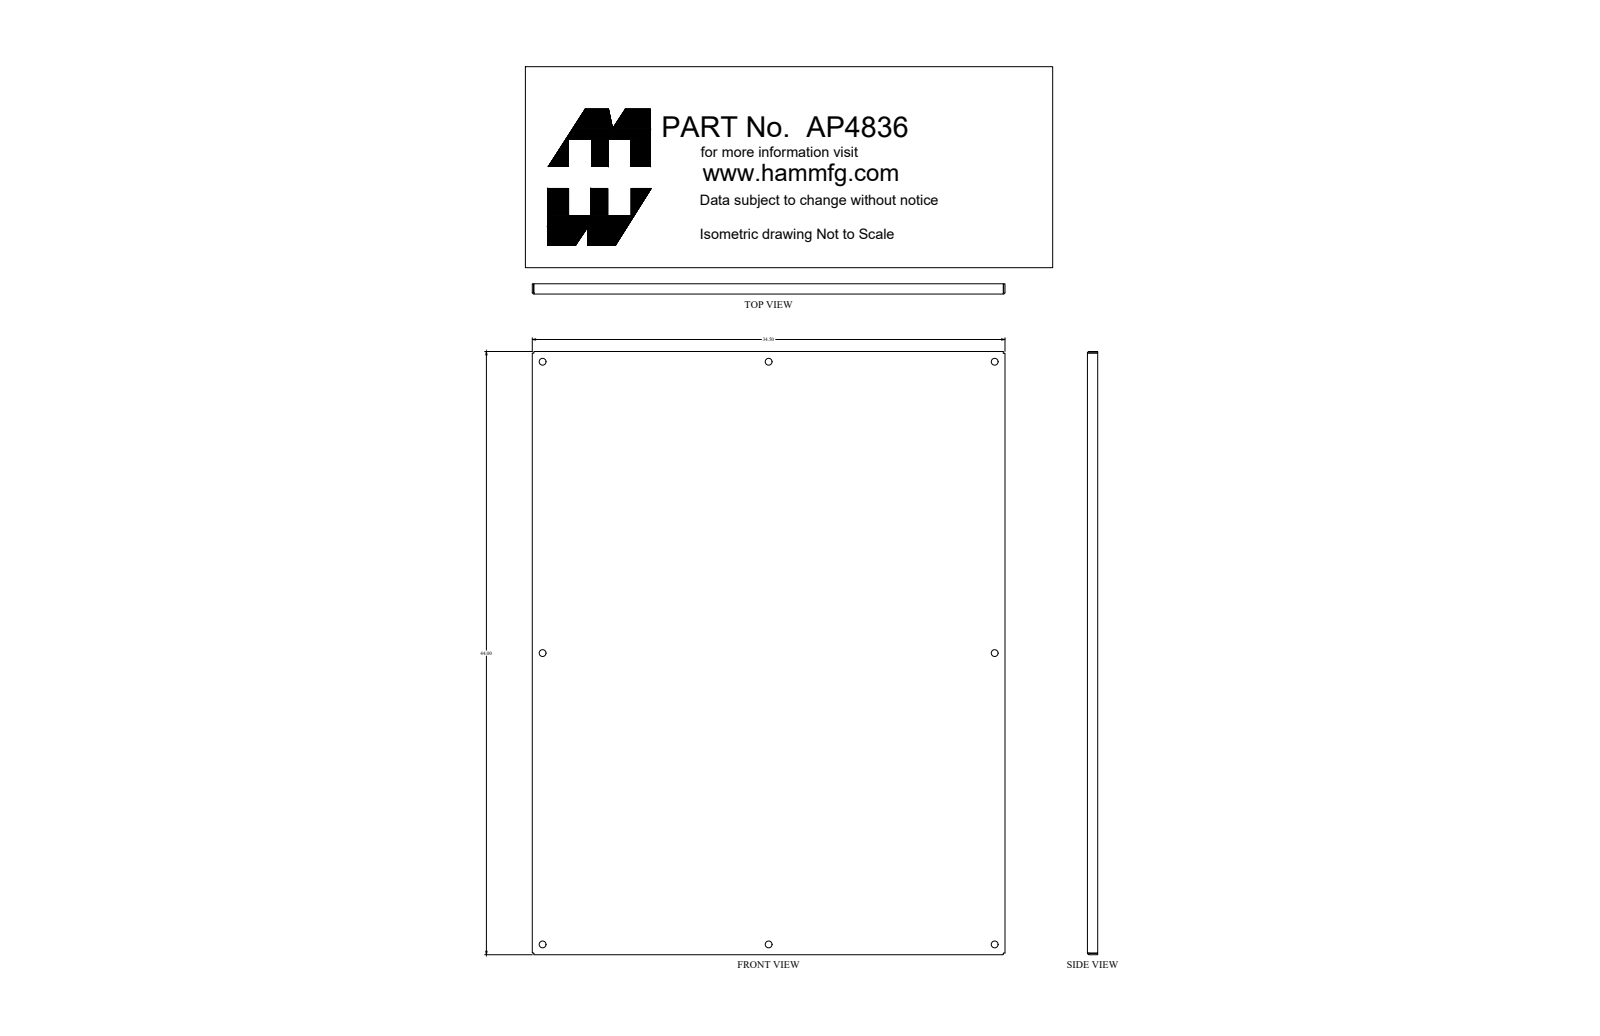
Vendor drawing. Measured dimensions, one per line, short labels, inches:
name: AP4836_Default
written by: SolidWorks 2019 (CONFIG_CONTROL_DESIGN)
unit: in
bodies: 1 solid, 46 faces (22 planar, 24 cylindrical, 0 other)
size: 44 × 34.5 × 0.75
volume: 153.3 in³; area: 3 243 in²
holes: 8× ⌀0.5
rounds: 4× R0.03, 4× R0.125
face distances: 0.095, 34.405, 43.905, 34.31, 34.5, 44, 43.81, 0.75, 0.655, 0.125
hole spacings: 16.499, 21.249, 26.902, 39.247, 45.588, 32.998, 42.498, 53.804
